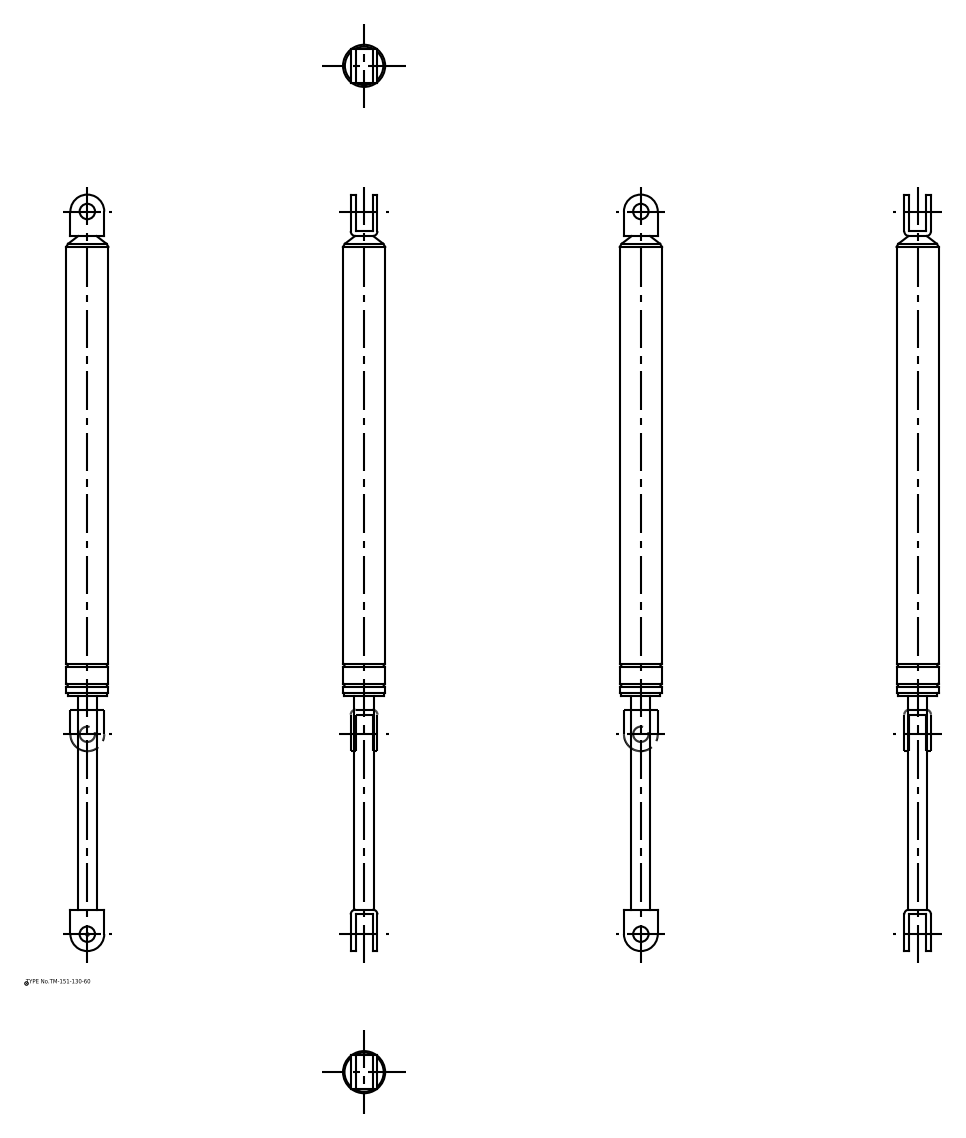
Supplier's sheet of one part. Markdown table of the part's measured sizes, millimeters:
| quantity | value |
| --- | --- |
| part name | TM_151_130_60; TM_151_130_60_div |
| STEP written by | spGate 16.7.1 (AUTOMOTIVE_DESIGN) |
| units | millimeters |
| bodies | 2 solids, 64 faces (22 planar, 32 cylindrical, 10 other) |
| overall size | 492 × 28.2 × 28.2 |
| volume | 199 066 mm³ |
| surface area | 37 978 mm² |
| round holes (diameter × count) | 10 × 2 |
| round bosses / shafts (diameter × count) | 28.2 × 1, 27.4 × 1, 25.5 × 1, 12.5 × 1 |
| partial cylindrical surfaces (radius × count) | 3.2 × 4, 11 × 2 |
| main face-to-face distances | 3.2, 14.2, 17.4, 11, 22, 441.2, 142.2, 444.4, 302.2, 299 |
| hole center spacings | 470 |
